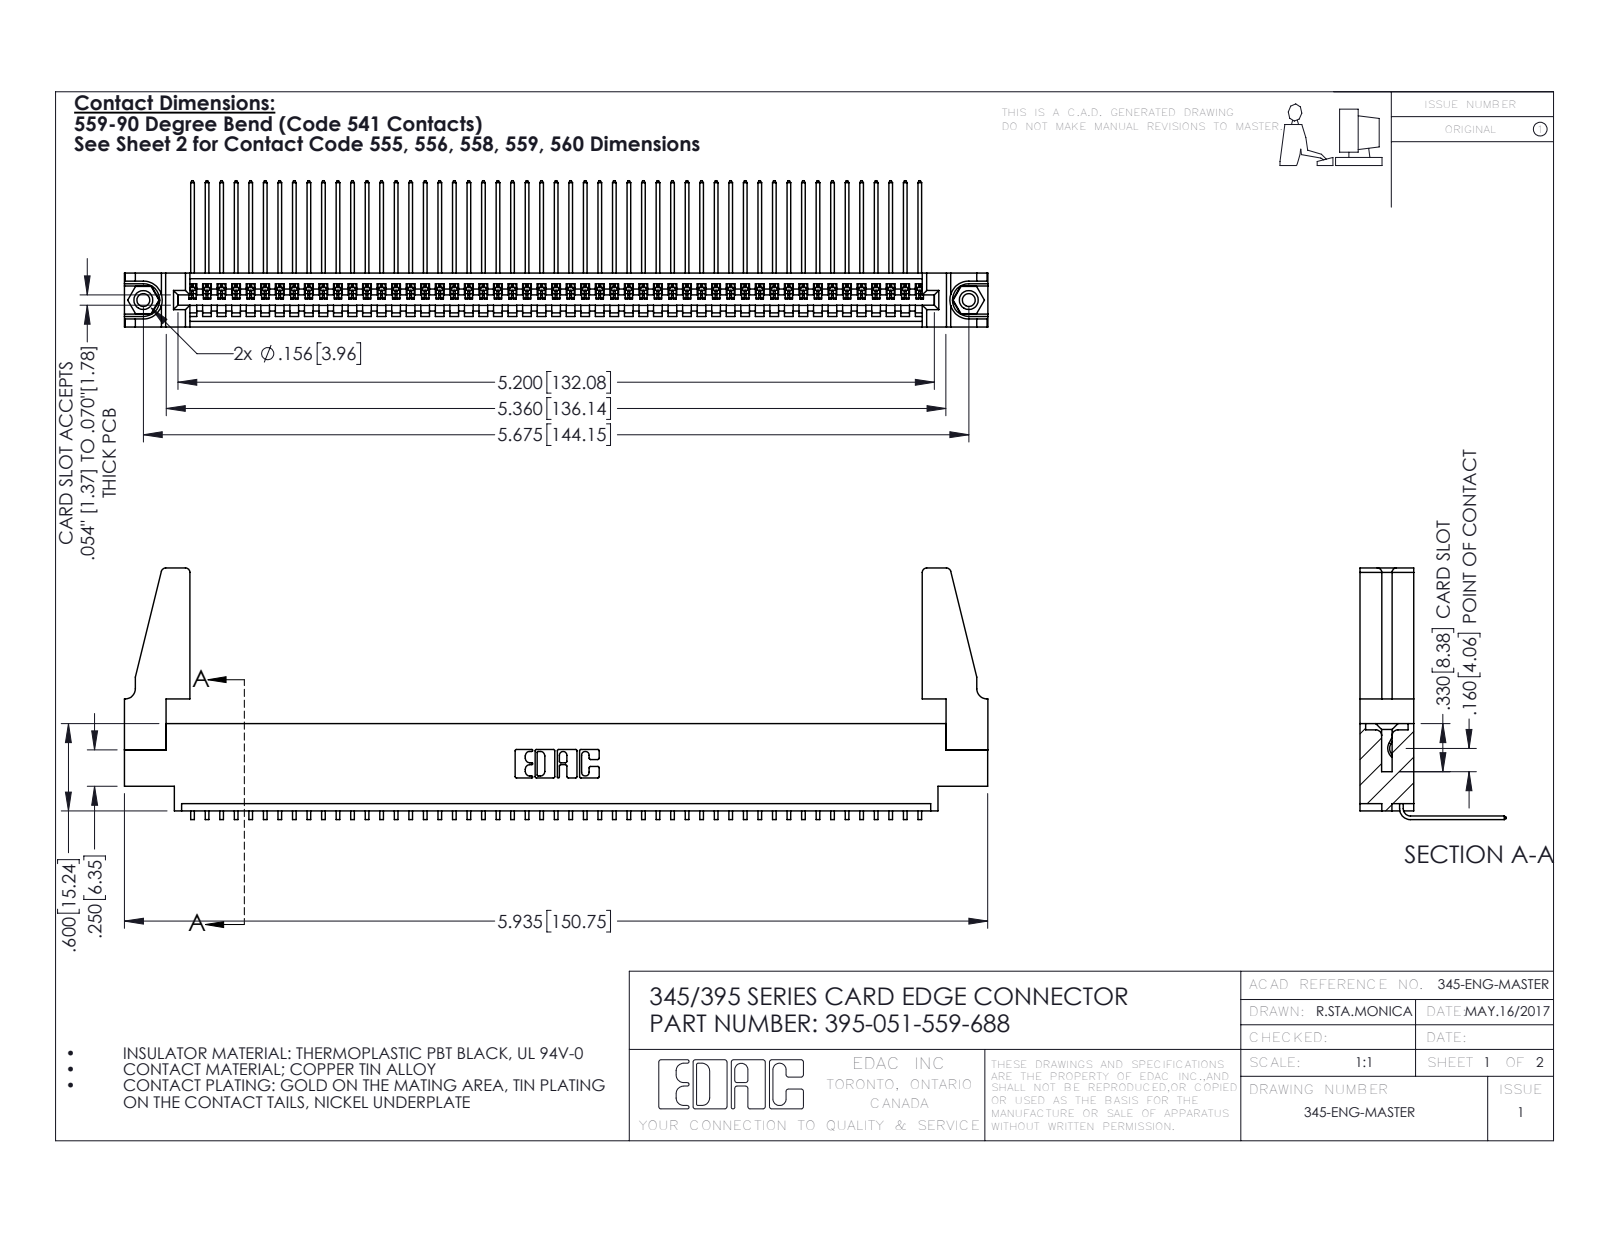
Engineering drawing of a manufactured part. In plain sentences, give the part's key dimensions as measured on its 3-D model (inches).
The part is named "395-051-559-688; 345-250-001_345-250-001-102; 345-292-001_558 559 Tail - 1; 345-220-078_345-220-088 (+1 more)". Its 3-D file was written by "SolidWorks 2016 (CONFIG_CONTROL_DESIGN)". It is 56 solids with 3314 faces: 2298 planar, 1000 cylindrical and 16 other. Overall it measures 5.936 by 1.729 by 1.005 inches. Its volume is 1.08 cubic inches and its surface area 36.55 square inches. Round holes: 2 of diameter 0.089, 2 of diameter 0.125, 2 of diameter 0.156, 1 of diameter 0.064. Round bosses or shafts: 2 of diameter 0.155. Partial cylindrical surfaces (rounded edges, fillets, slot ends): 102 of radius 0.006, 22 of radius 0.01, 8 of radius 0.03, 6 of radius 0.007, 6 of radius 0.031, 3 of radius 0.026, 2 of radius 0.031, 2 of radius 0.04. The main face-to-face distances are 0.072, 0.37, 0.298, 0.2, 0.098, 0.272, 0.025, 0.225, 0.175, 0.149. The hole center spacings are 0.27, 5.439, 5.675.
